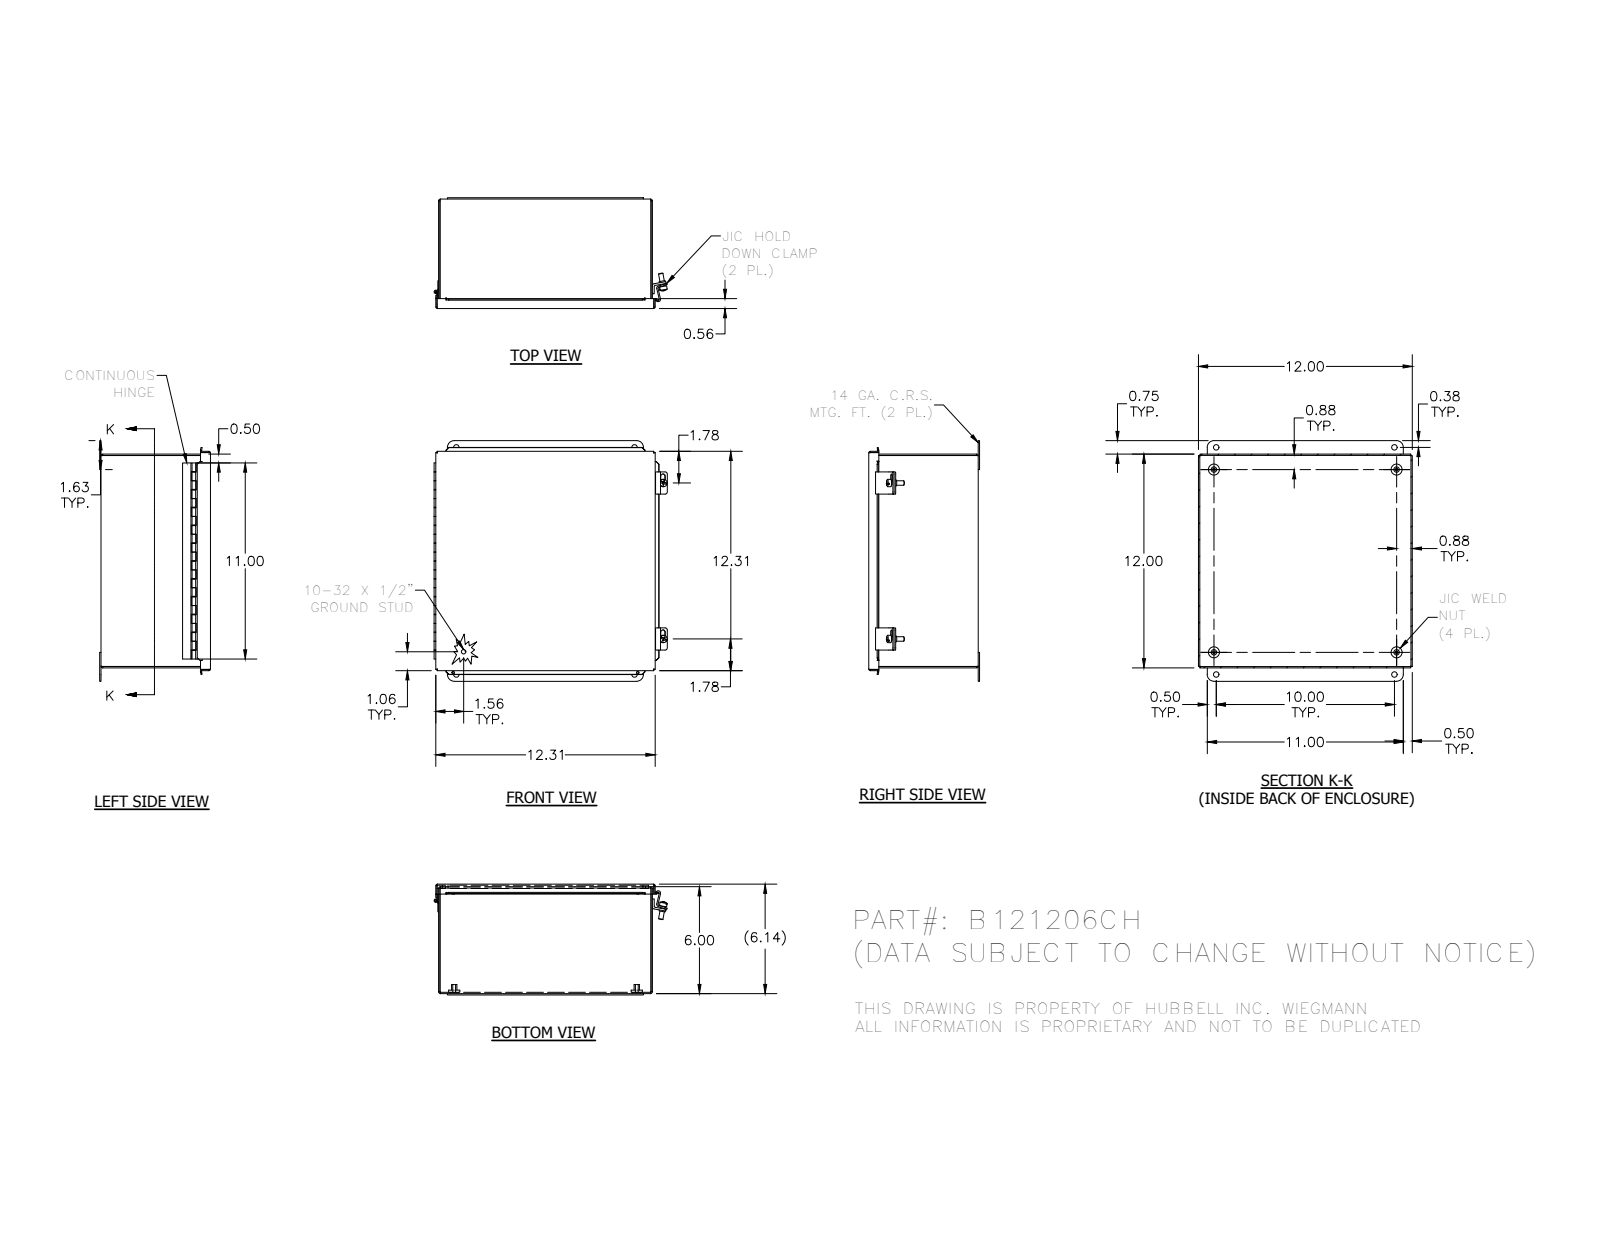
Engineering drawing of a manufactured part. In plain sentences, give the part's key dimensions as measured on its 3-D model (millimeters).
The part is named "B121206CH; 3499; 3485; C1001 (+8 more)". Its 3-D file was written by "Autodesk Inventor 2012 (AUTOMOTIVE_DESIGN)". It is 20 solids with 499 faces: 323 planar, 131 cylindrical and 45 other. Overall it measures 342.9 by 332.4 by 158 millimeters. Its volume is 876 500 cubic millimeters and its surface area 946 400 square millimeters. Round holes: 4 of diameter 4, 4 of diameter 7.9, 2 of diameter 3.6, 2 of diameter 5, 1 of diameter 2.9. Round bosses or shafts: 4 of diameter 15.9, 4 of diameter 7.6, 3 of diameter 6.4, 2 of diameter 10.4, 2 of diameter 8.7, 1 of diameter 5.1, 1 of diameter 4.8, 1 of diameter 2.5. Partial cylindrical surfaces (rounded edges, fillets, slot ends): 15 of radius 0.8, 8 of radius 2.7, 8 of radius 3.2, 7 of radius 2.4, 4 of radius 3.4, 4 of radius 9.5, 3 of radius 1.6, 3 of radius 3.2. The main face-to-face distances are 1.9, 302.9, 154.5, 1.6, 156.1, 152.6, 154.2, 304.8, 301, 1.9. The hole center spacings are 292.1, 31.9, 254, 259.1, 259.1, 260.4, 368.2, 389.2.
